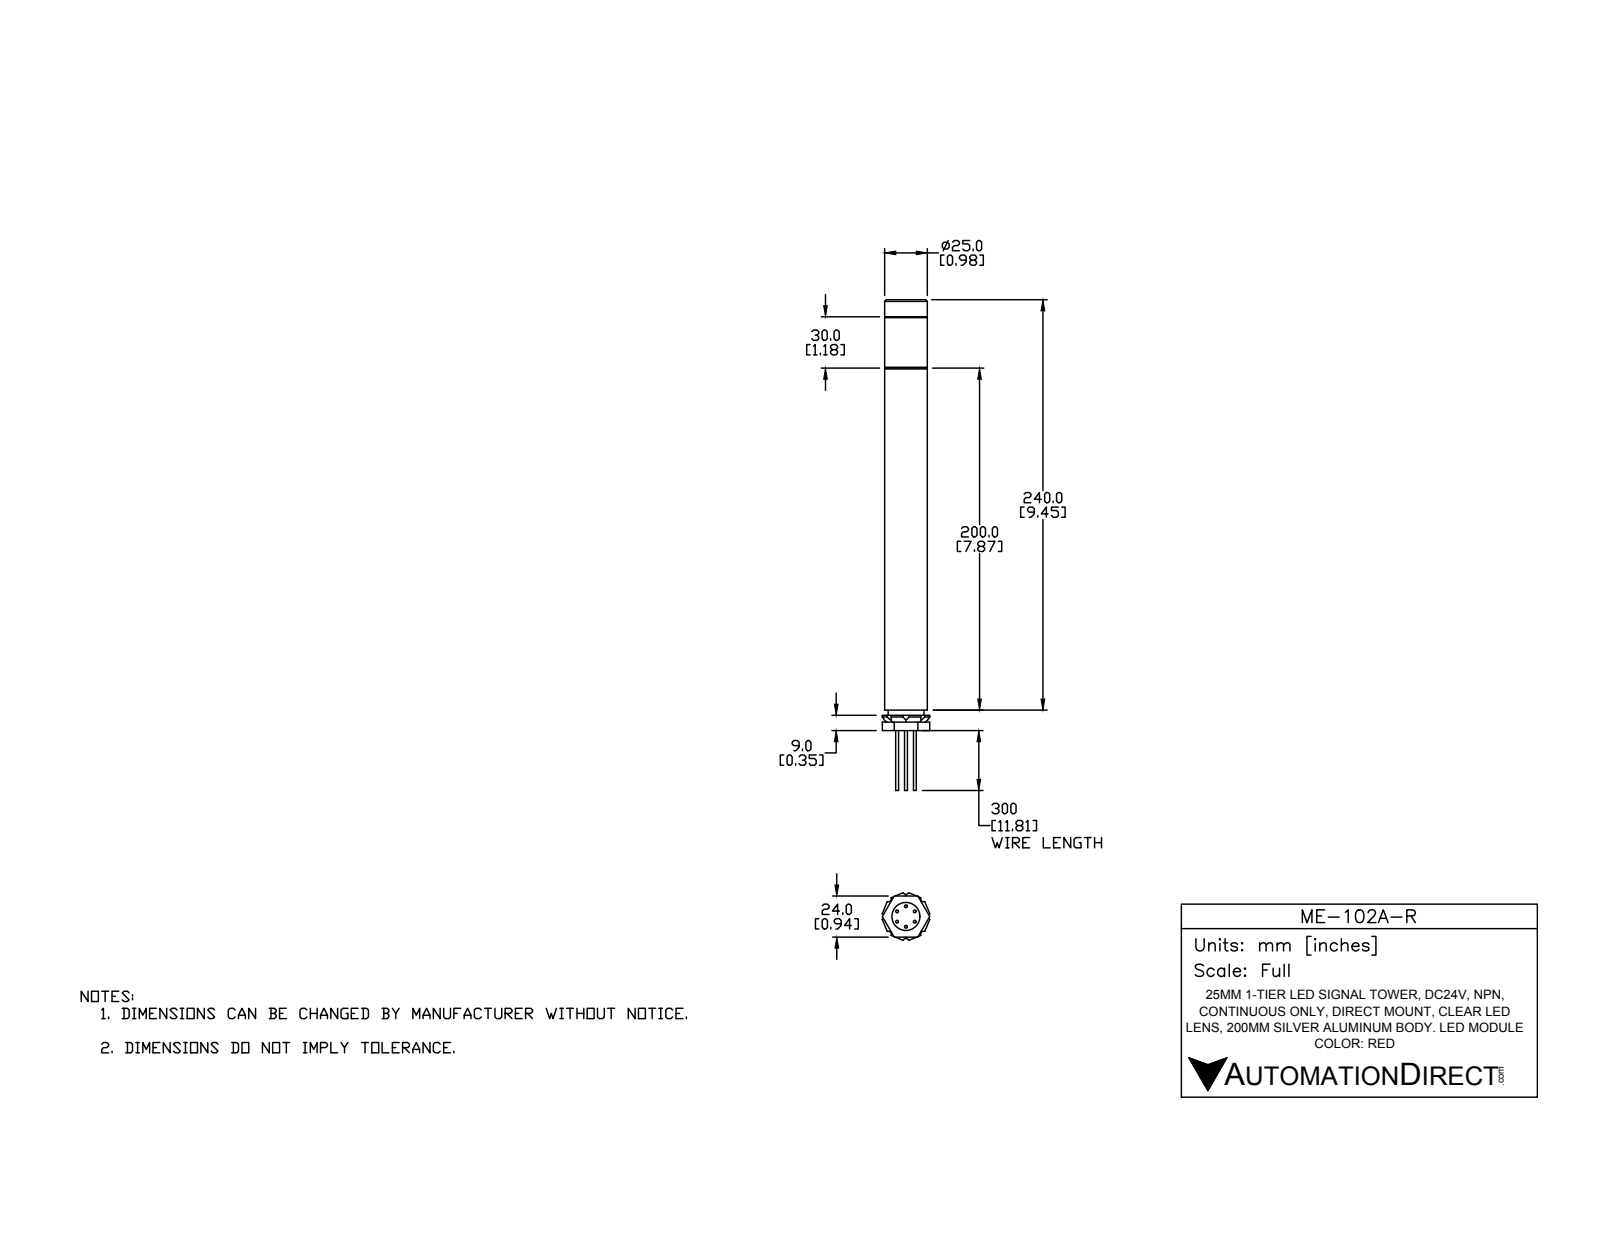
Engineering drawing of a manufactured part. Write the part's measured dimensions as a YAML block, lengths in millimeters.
part_name: "ME-102A-R"
step_written_by: "SolidWorks 2016 (AUTOMOTIVE_DESIGN)"
units: millimeters
bodies: {solids: 12, faces: 132, planar: 71, cylindrical: 47, other: 14}
overall_size: [287, 27.89, 27.89]
volume: 112181
surface_area: 31231
round_holes:
  - {diameter: 3.2, count: 1}
  - {diameter: 7.7, count: 1}
  - {diameter: 16.4, count: 1}
  - {diameter: 18, count: 1}
  - {diameter: 20.7, count: 1}
  - {diameter: 21, count: 1}
round_bosses_or_shafts:
  - {diameter: 1.7, count: 6}
  - {diameter: 25, count: 1}
  - {diameter: 20.9, count: 1}
  - {diameter: 16, count: 1}
  - {diameter: 5, count: 1}
partial_cylinders:
  - {radius: 1.75, count: 8}
face_to_face_distances: [30, 40, 207, 167, 197, 10, 45, 212, 242, 252]
